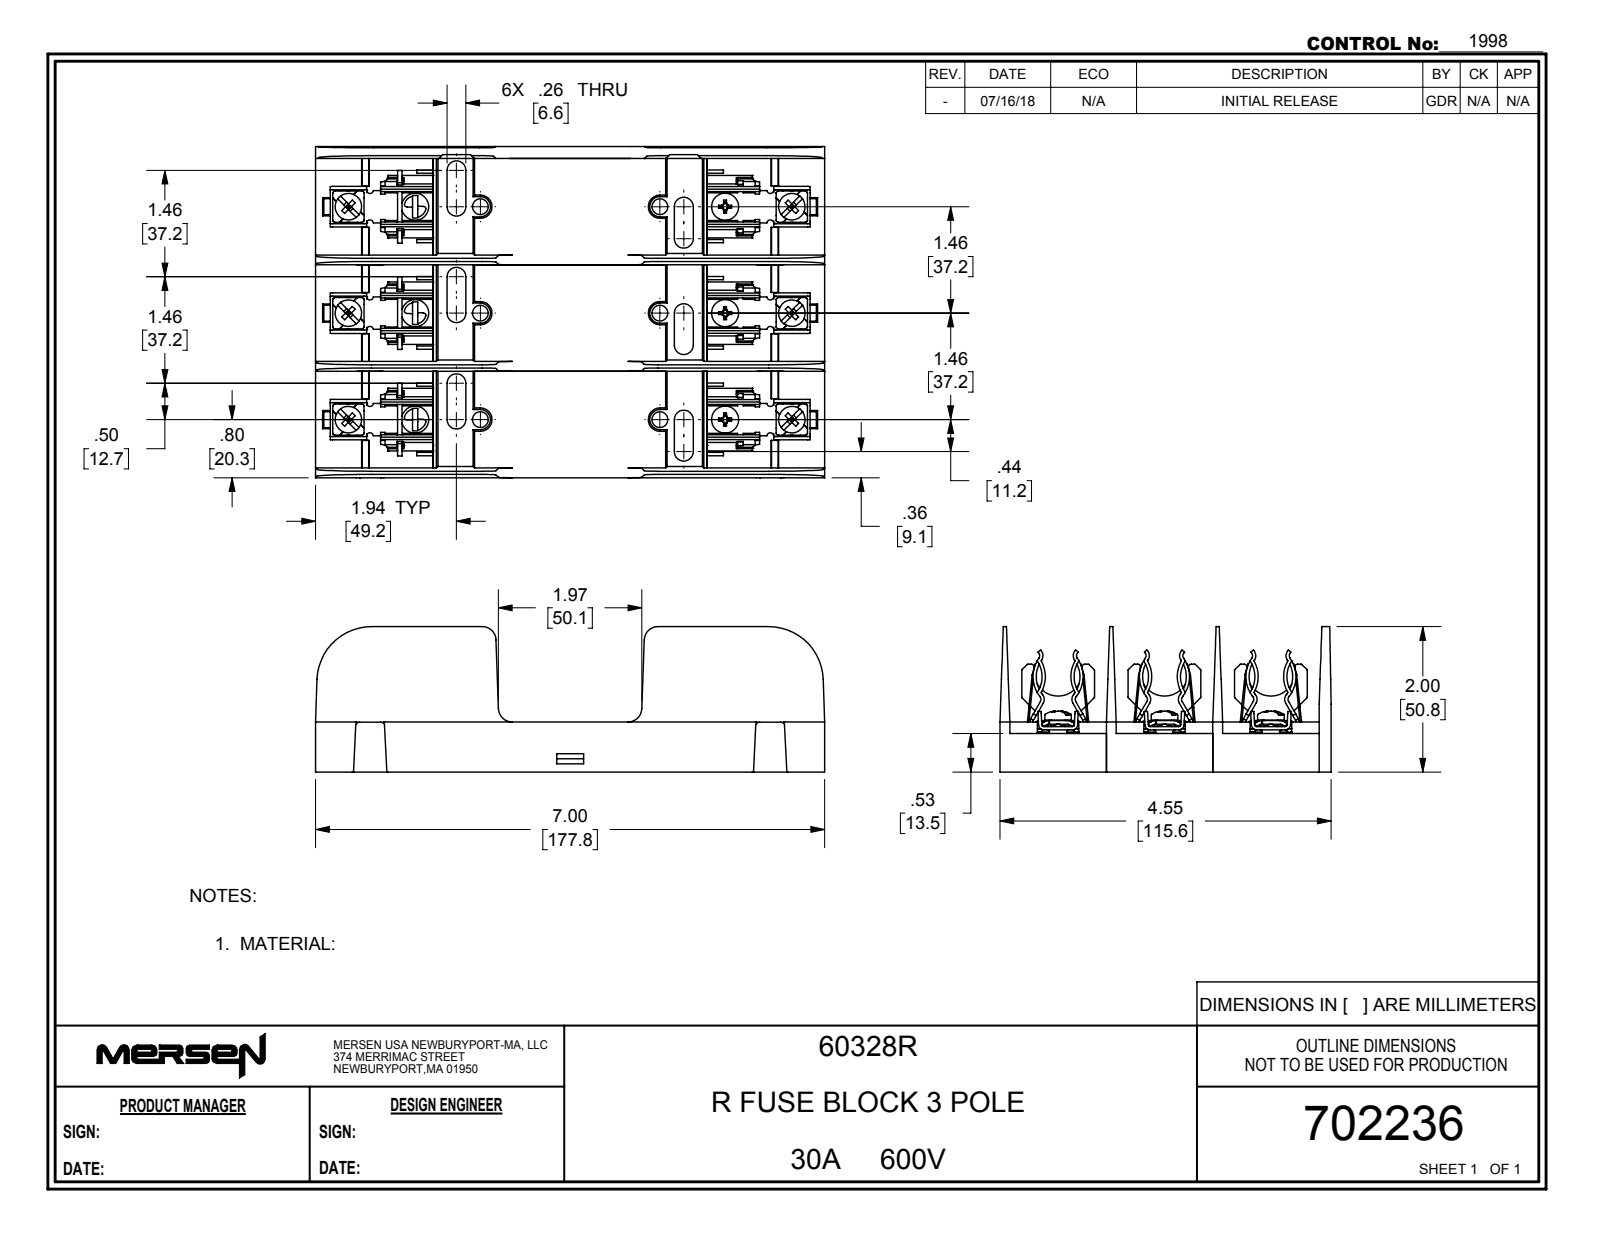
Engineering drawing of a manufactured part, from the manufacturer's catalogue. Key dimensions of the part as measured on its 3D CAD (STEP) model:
Part name (STEP PRODUCT): 702236rev
STEP written by: SolidWorks 2017 (AUTOMOTIVE_DESIGN)
Units: inches
Bodies: 37 solids, 3213 faces (1885 planar, 833 cylindrical, 495 other)
Overall size (bounding box): 7 × 4.553 × 2
Volume: 12.61 in³ · Surface area: 280.8 in²
Round holes (diameter × count): ⌀0.159 ×6, ⌀0.218 ×6
Round bosses / shafts (diameter × count): ⌀0.373 ×6, ⌀0.239 ×6, ⌀0.19 ×6, ⌀0.156 ×6, ⌀0.365 ×4, ⌀0.115 ×3, ⌀0.365 ×2
Partial cylindrical surfaces — rounded edges, fillets, slot ends (radius × count): R0.01 ×50, R0.02 ×38, R0.004 ×36, R0.02 ×36, R0.07 ×36, R0.015 ×34, R0.03 ×30, R0.032 ×24
Main face-to-face distances: 1.461, 1.463, 2.926, 0.53, 0.02, 0.16, 0.69, 1.462, 2.923, 2.923
Hole centre spacings: 1.463, 2.331, 4.526, 1.815, 4.283, 2.869, 2.926, 3.443
